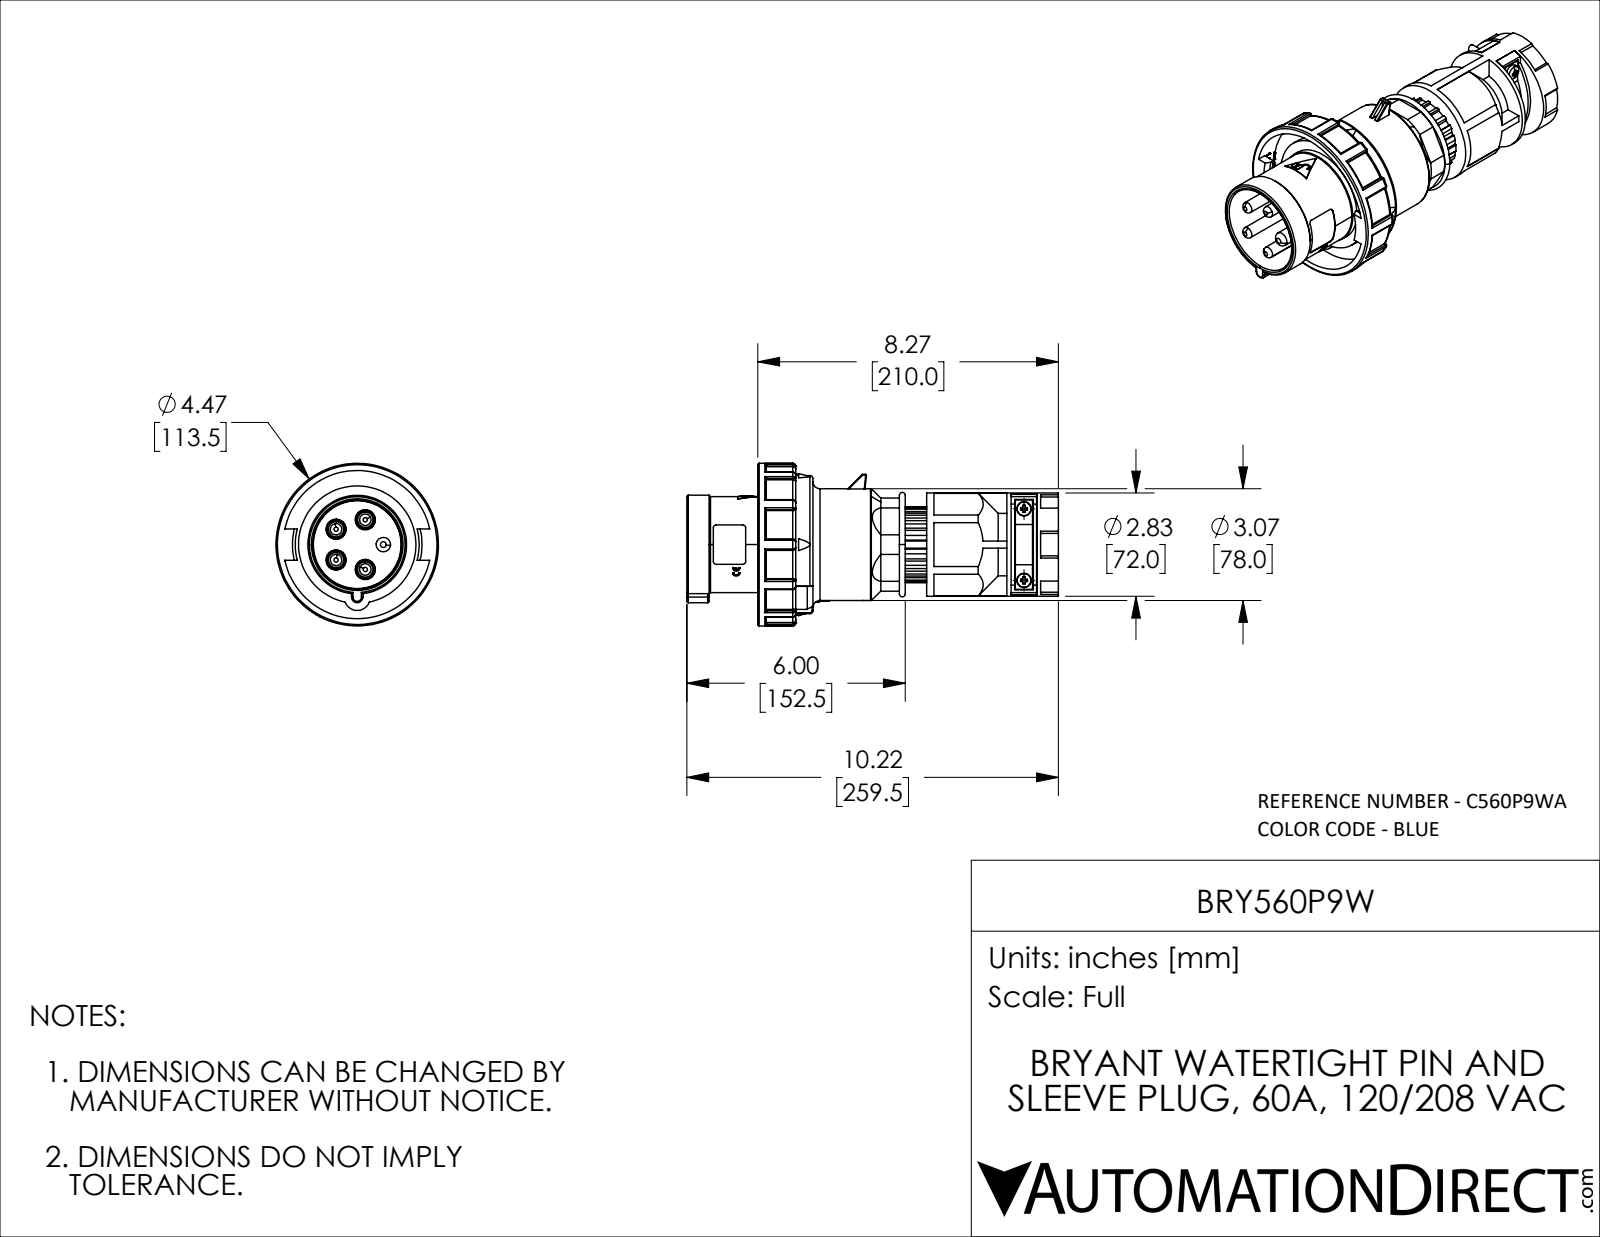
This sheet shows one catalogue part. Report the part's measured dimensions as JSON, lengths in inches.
{"part_name": "BRY560P9W", "step_written_by": "SolidWorks 2021 (CONFIG_CONTROL_DESIGN)", "units": "inches", "bodies": {"solids": 8, "faces": 1184, "planar": 490, "cylindrical": 388, "other": 306}, "overall_size": [10.217, 4.469, 4.469], "volume_in3": 46.24, "surface_area_in2": 244.8, "round_holes": [[0.079, 2], [0.197, 2], [1.457, 1], [2.441, 1], [2.579, 1], [4.075, 1]], "round_bosses_or_shafts": [[0.315, 4], [4.469, 1], [3.228, 1], [3.071, 1], [2.835, 1], [2.713, 1], [2.678, 1], [2.638, 1]], "partial_cylinders_radius": [[0.039, 34], [0.02, 23], [0.079, 18], [1.358, 6], [0.016, 4], [0.118, 3], [0.157, 3], [0.047, 2]], "face_to_face_distances": [3.386, 2.913, 6.299, 2.559, 0.591, 3.622, 0.197, 0.709, 0.118, 3.819], "hole_center_spacings": [1.969]}
